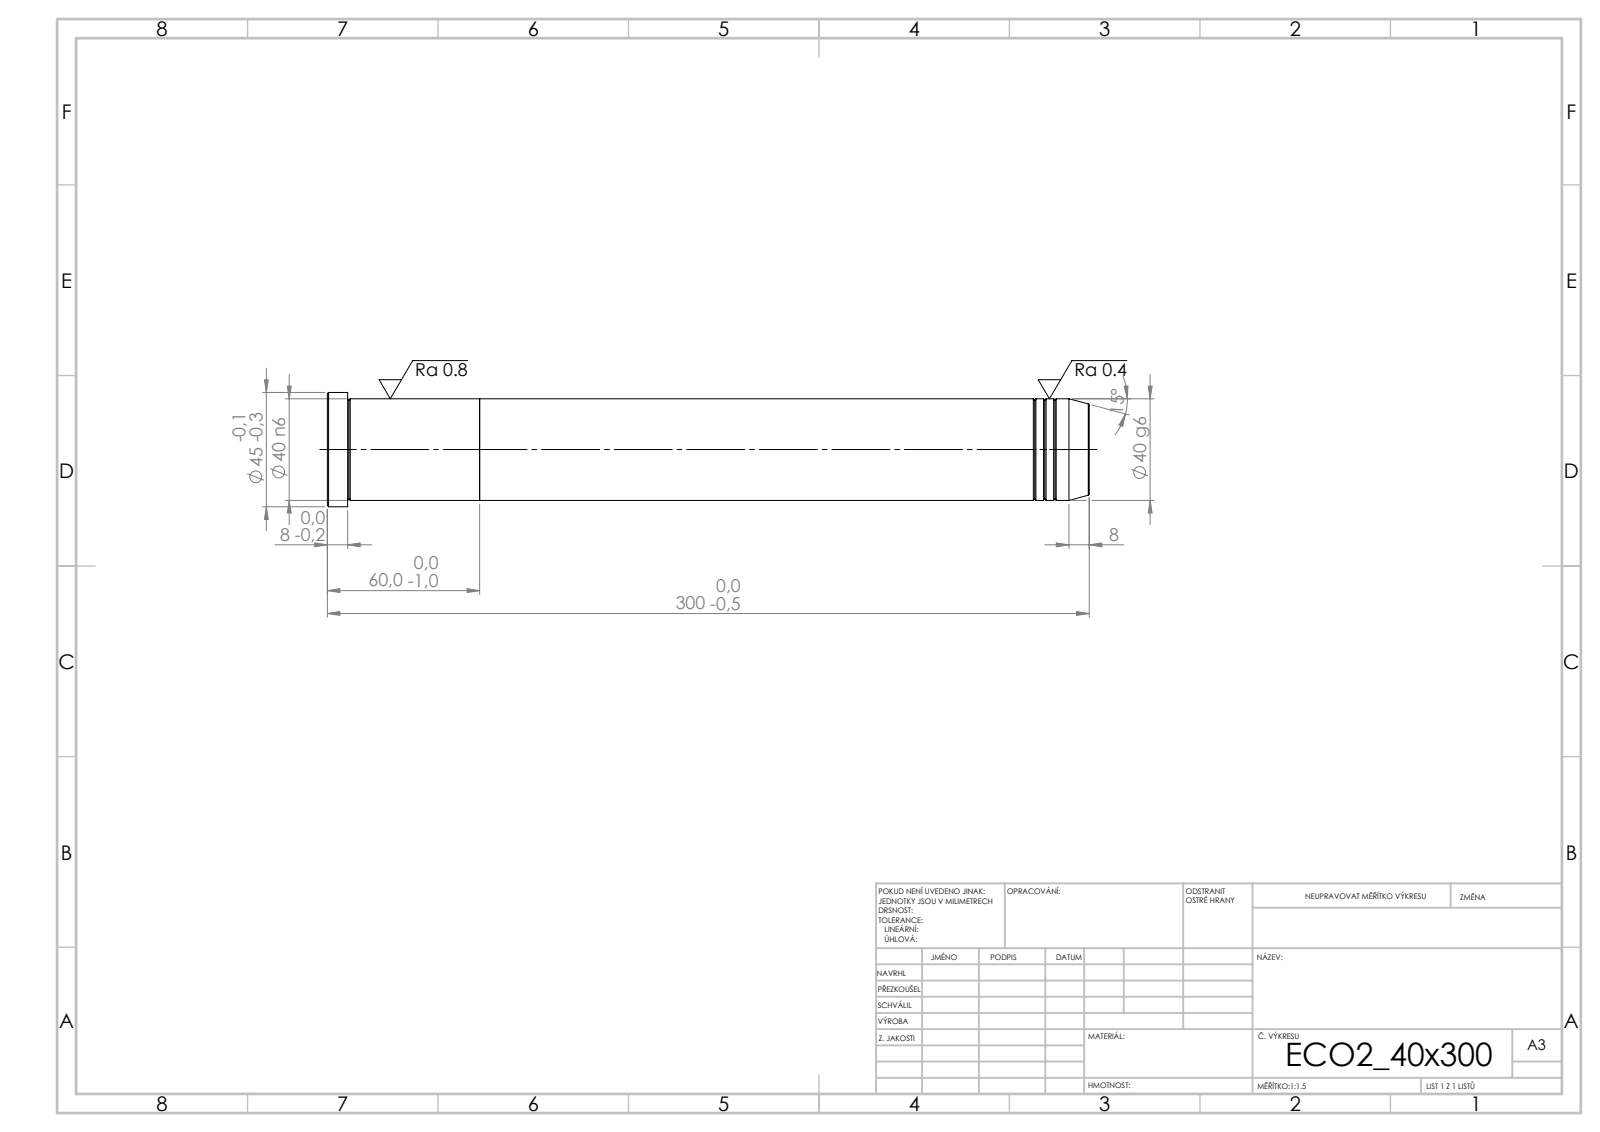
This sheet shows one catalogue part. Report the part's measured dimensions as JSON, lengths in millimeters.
{"step_written_by": "SolidWorks 2019 (CONFIG_CONTROL_DESIGN)", "units": "millimeters", "bodies": {"solids": 2, "faces": 39, "planar": 5, "cylindrical": 12, "other": 22}, "overall_size": [300, 45, 45], "volume_mm3": 378406, "surface_area_mm2": 43464, "round_bosses_or_shafts": [[45, 1], [40, 1]], "face_to_face_distances": [60, 240, 300, 292, 52, 8]}
